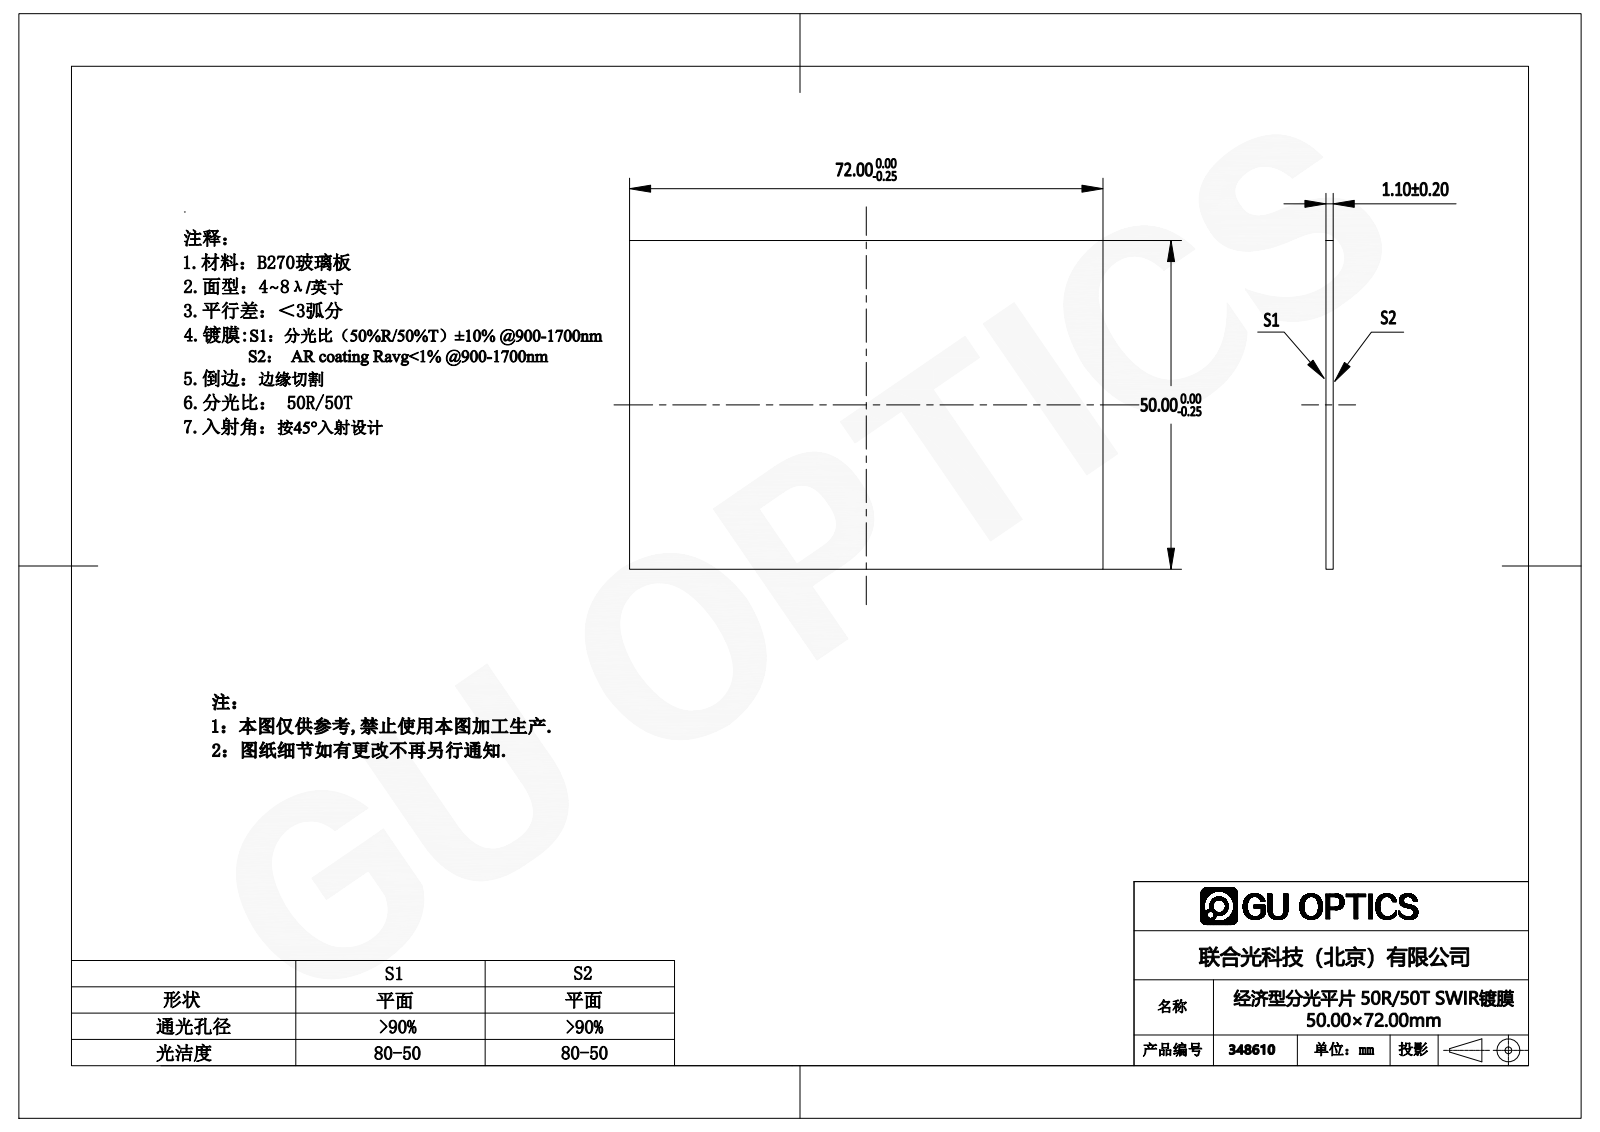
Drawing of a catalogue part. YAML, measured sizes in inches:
part_name: "348512"
step_written_by: "SolidWorks 2016 (CONFIG_CONTROL_DESIGN)"
units: inches
bodies: {solids: 1, faces: 6, planar: 6, cylindrical: 0, other: 0}
overall_size: [2.835, 1.969, 0.043]
volume: 0.242
surface_area: 11.58
face_to_face_distances: [0.043, 1.969, 2.835]
